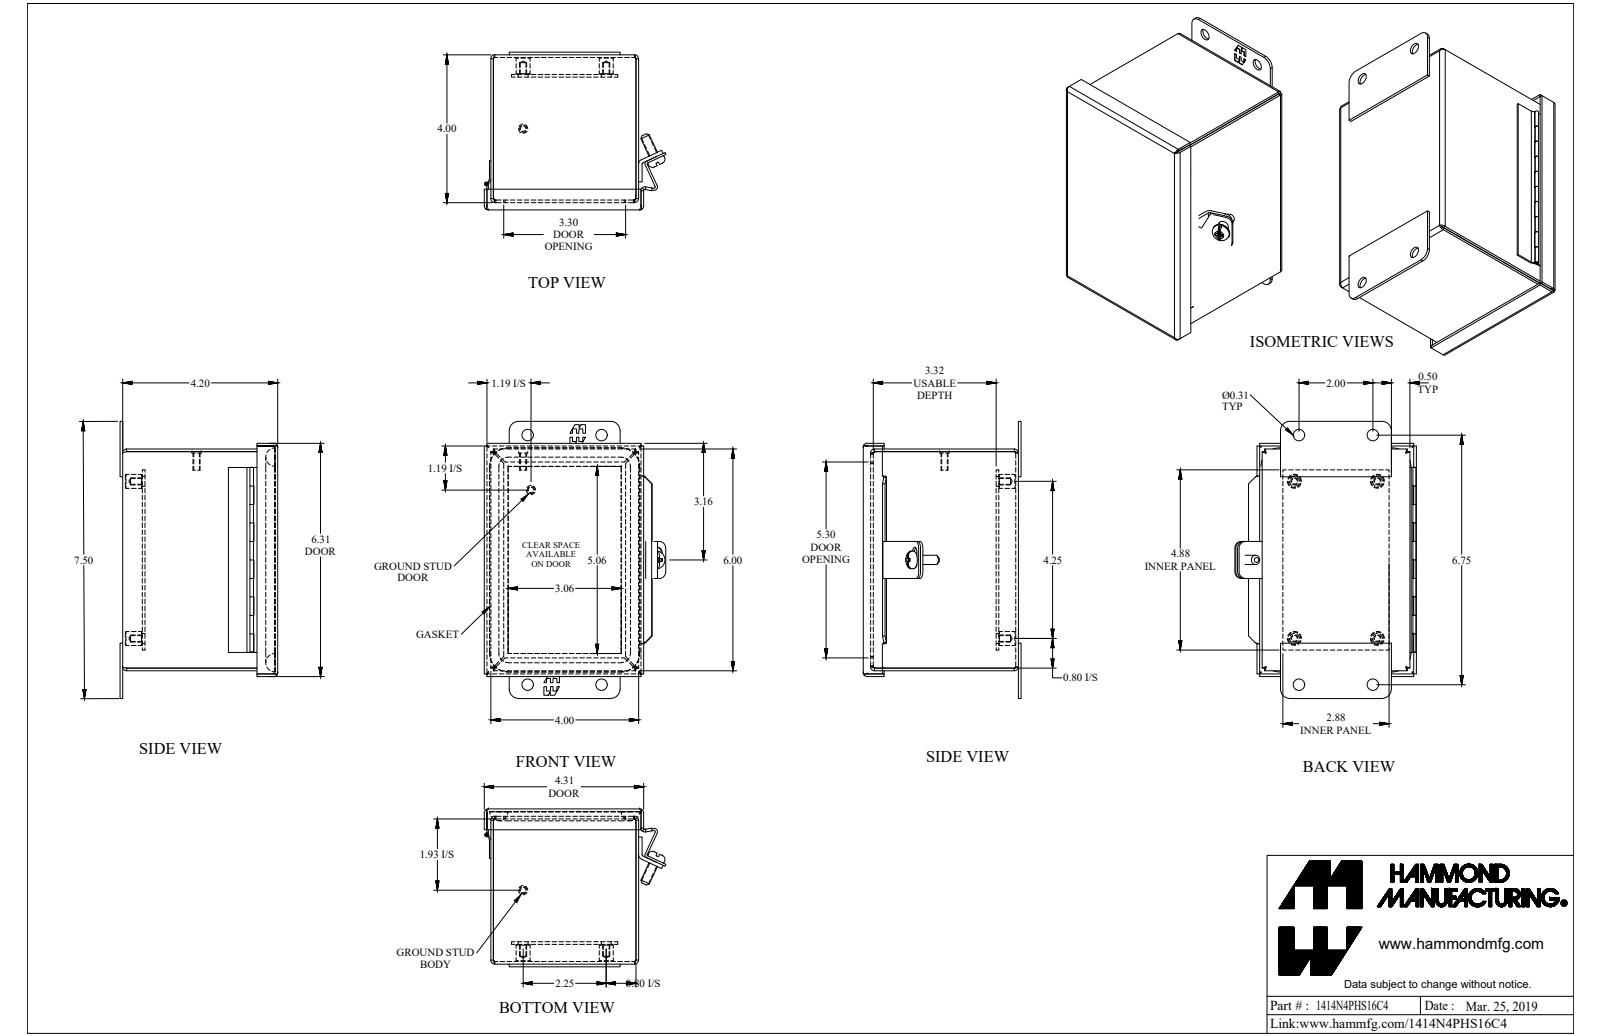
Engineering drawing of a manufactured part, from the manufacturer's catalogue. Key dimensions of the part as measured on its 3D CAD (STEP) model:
Part name (STEP PRODUCT): 1414N4PHS16C4
STEP written by: SolidWorks 2018 (AUTOMOTIVE_DESIGN)
Units: inches
Bodies: 18 solids, 462 faces (278 planar, 133 cylindrical, 51 other)
Overall size (bounding box): 7.5 × 4.903 × 4.269
Volume: 14.62 in³ · Surface area: 405.4 in²
Round holes (diameter × count): ⌀0.156 ×4, ⌀0.265 ×4, ⌀0.313 ×4, ⌀0.05 ×1, ⌀0.213 ×1
Round bosses / shafts (diameter × count): ⌀0.375 ×4, ⌀0.25 ×3, ⌀0.19 ×2, ⌀0.48 ×1, ⌀0.1 ×1, ⌀0.045 ×1
Partial cylindrical surfaces — rounded edges, fillets, slot ends (radius × count): R0.25 ×20, R0.036 ×8, R0.108 ×8, R0.037 ×4, R0.079 ×4, R0.118 ×4, R0.188 ×4, R0.499 ×4
Main face-to-face distances: 0.072, 3.928, 0.081, 4, 5.928, 0.532, 3.856, 4.197, 4.116, 4.125
Hole centre spacings: 2.25, 1.257, 4.809, 5.502, 2.465, 2.466, 5.896, 1.256
